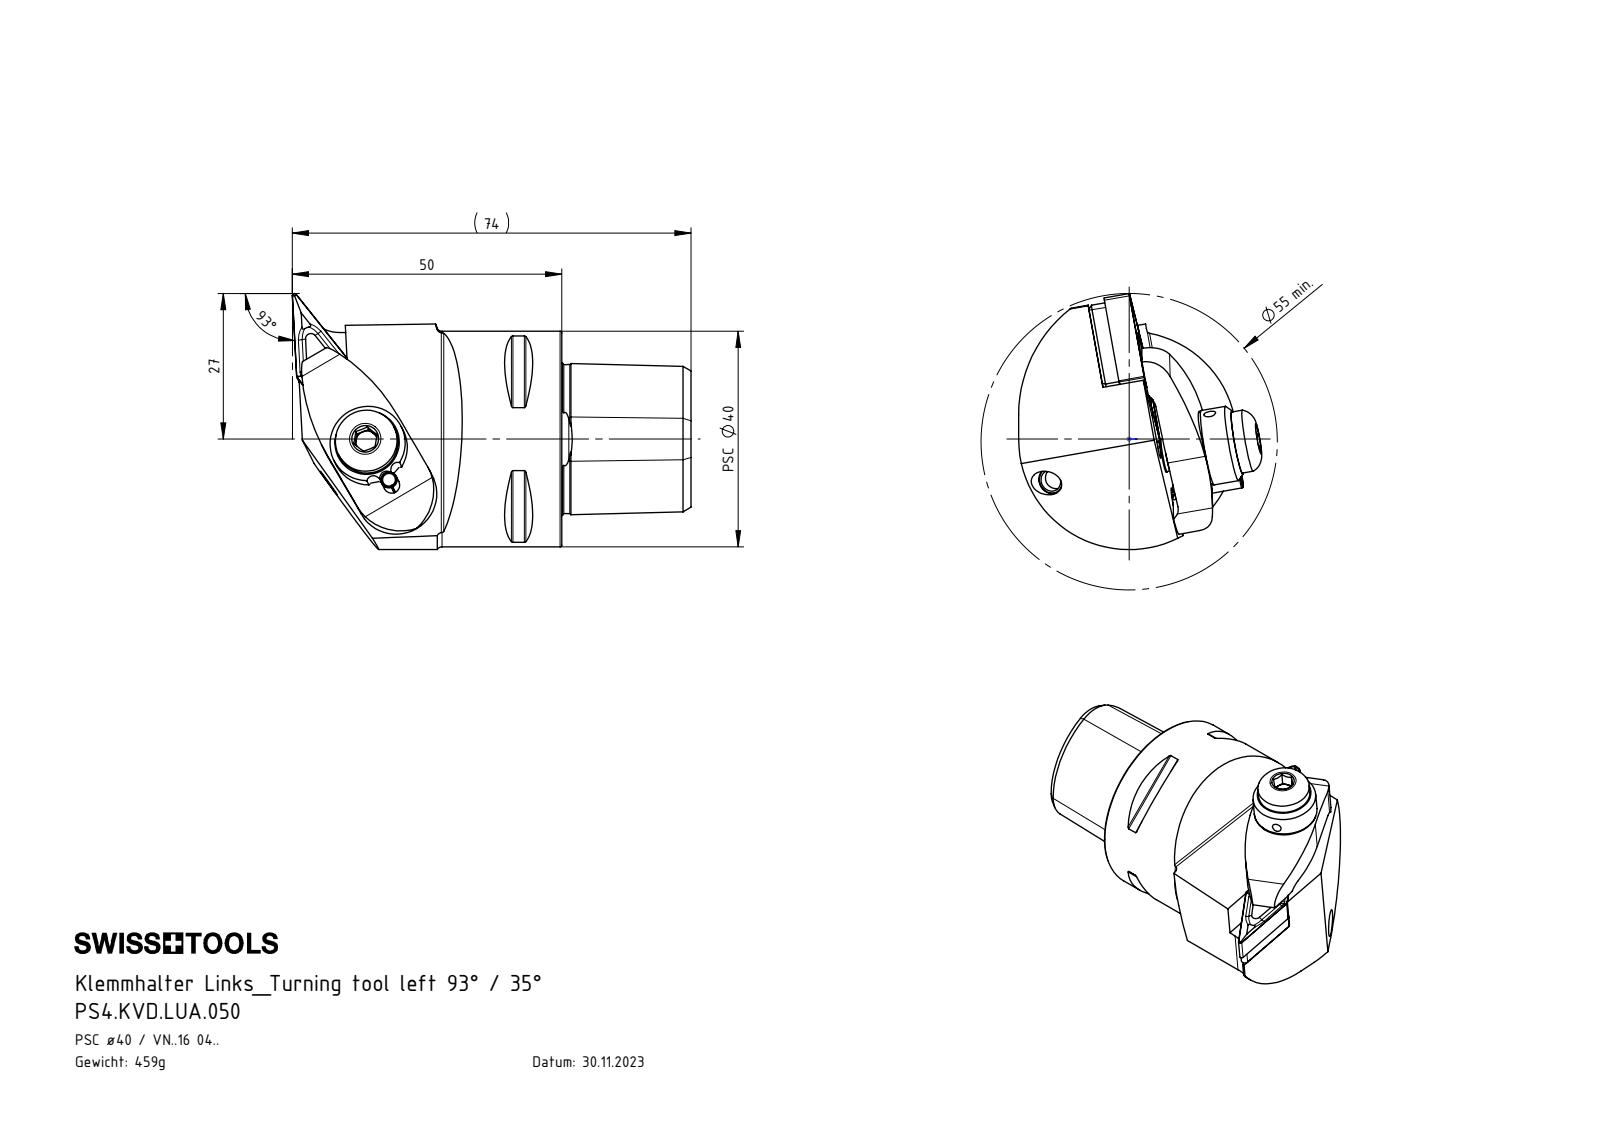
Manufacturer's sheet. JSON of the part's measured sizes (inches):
{"part_name": "WCC-ER5.102.012_B; WVD-ER2.101.003_A; VNMG160404; PS4-KVD.LUA.050_A (+6 more)", "step_written_by": "SolidWorks 2017 (AUTOMOTIVE_DESIGN)", "units": "inches", "bodies": {"solids": 10, "faces": 431, "planar": 100, "cylindrical": 131, "other": 200}, "overall_size": [2.914, 1.87, 1.776], "volume_in3": 3.537, "surface_area_in2": 28.62, "round_holes": [[0.079, 3], [0.157, 2], [0.197, 2], [0.276, 2], [0.094, 1], [0.118, 1], [0.13, 1], [0.15, 1], [0.165, 1], [0.181, 1], [0.195, 1], [0.244, 1]], "round_bosses_or_shafts": [[0.197, 2], [1.575, 1], [0.551, 1], [0.453, 1], [0.276, 1], [0.268, 1], [0.244, 1], [0.236, 1]], "partial_cylinders_radius": [[0.012, 8], [0.015, 6], [0.027, 6], [0.016, 4], [0.059, 3], [0.118, 3], [0.031, 2], [0.079, 2]], "face_to_face_distances": [0.36, 0.176, 0.051, 0.125, 0.301, 0.352, 0.227, 0.945, 0.375, 0.591], "hole_center_spacings": [0.316, 0.323, 0.751, 0.753, 0.758, 0.759, 0.76, 0.76]}
